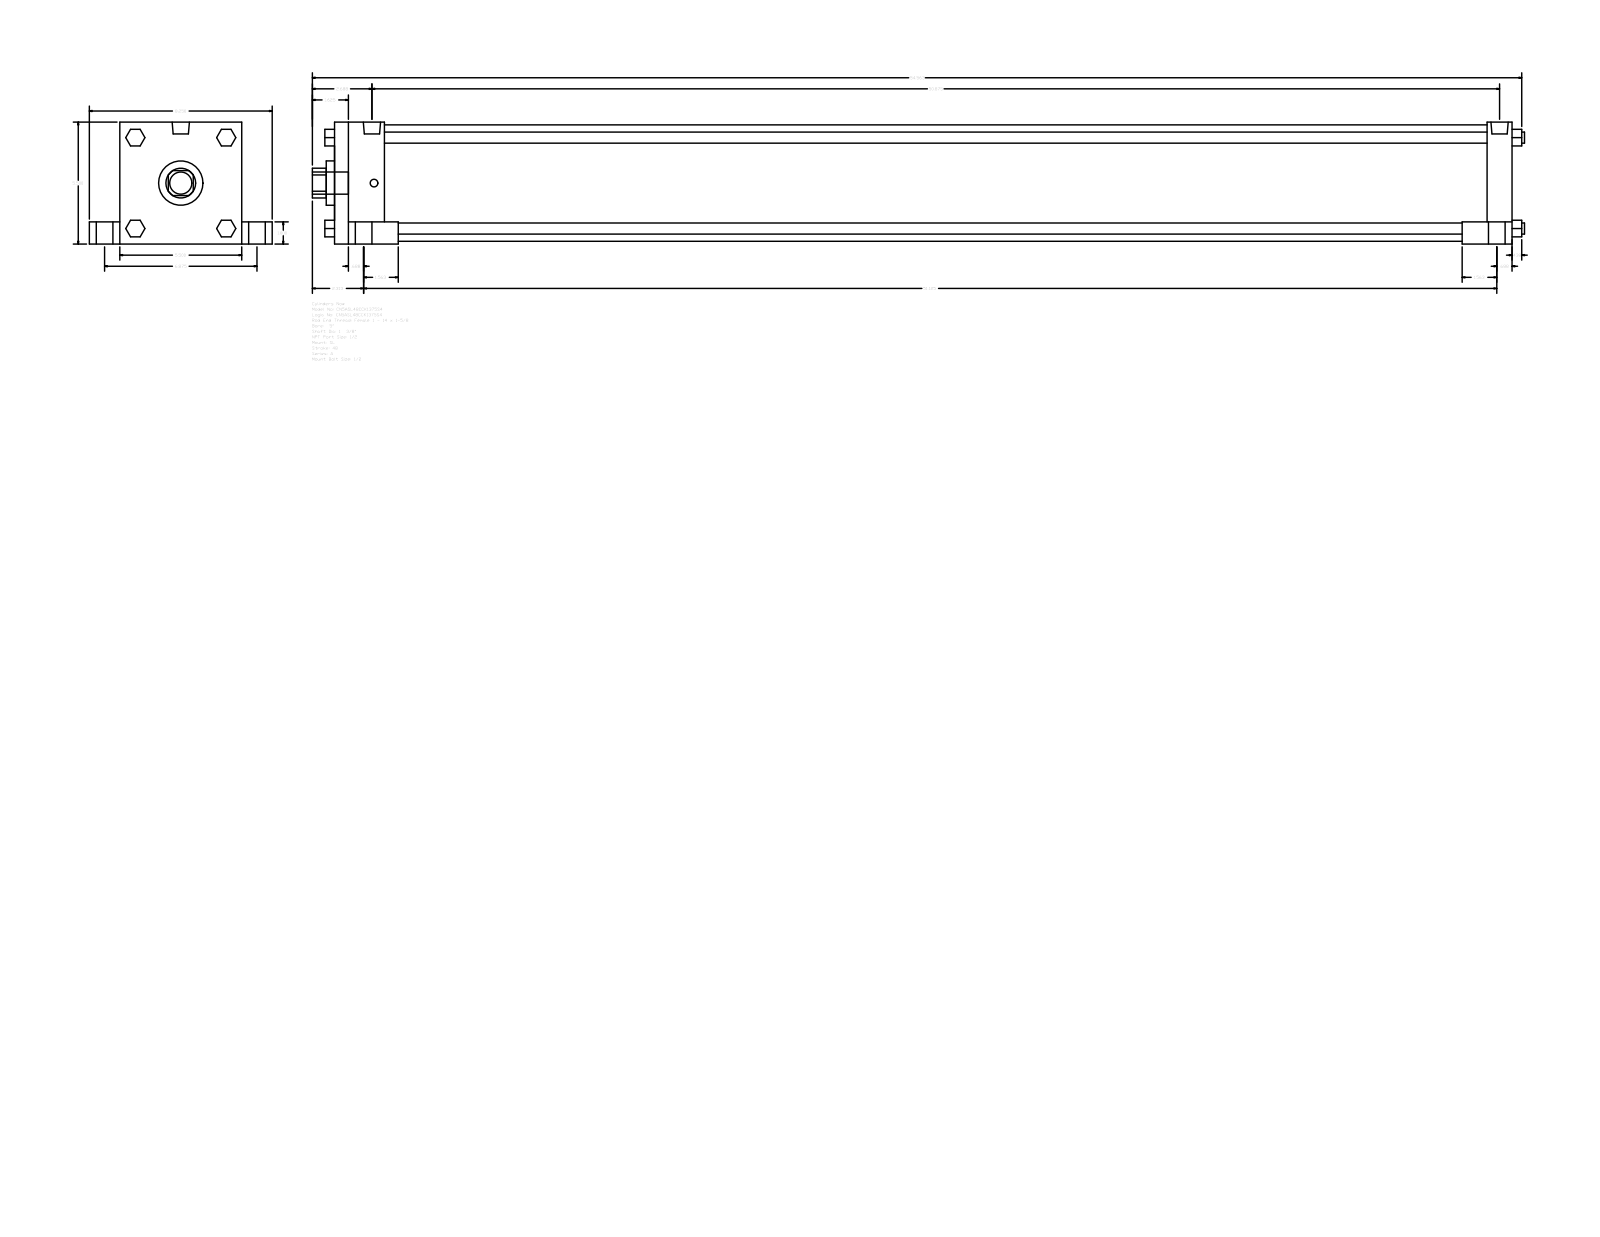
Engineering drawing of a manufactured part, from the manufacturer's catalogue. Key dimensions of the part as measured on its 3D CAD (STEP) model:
Part name (STEP PRODUCT): A_SL__0500_1.375
STEP written by: GSSL Pune (CONFIG_CONTROL_DESIGN)
Units: millimetres
Bodies: 0 solids, 150 faces (114 planar, 36 cylindrical, 0 other)
Overall size (bounding box): 1389.06 × 209.55 × 139.7
Round holes (diameter × count): ⌀34.92 ×1, ⌀50.8 ×1, ⌀133.35 ×1
Round bosses / shafts (diameter × count): ⌀25.4 ×5, ⌀19.05 ×4, ⌀12.7 ×4, ⌀8.73 ×4, ⌀19.77 ×2
Partial cylindrical surfaces — rounded edges, fillets, slot ends (radius × count): R17.06 ×1
Main face-to-face distances: 139.7, 1349.38, 28.58, 57.15, 25.4, 114.3, 34.93, 174.63, 1320.8, 1263.65
